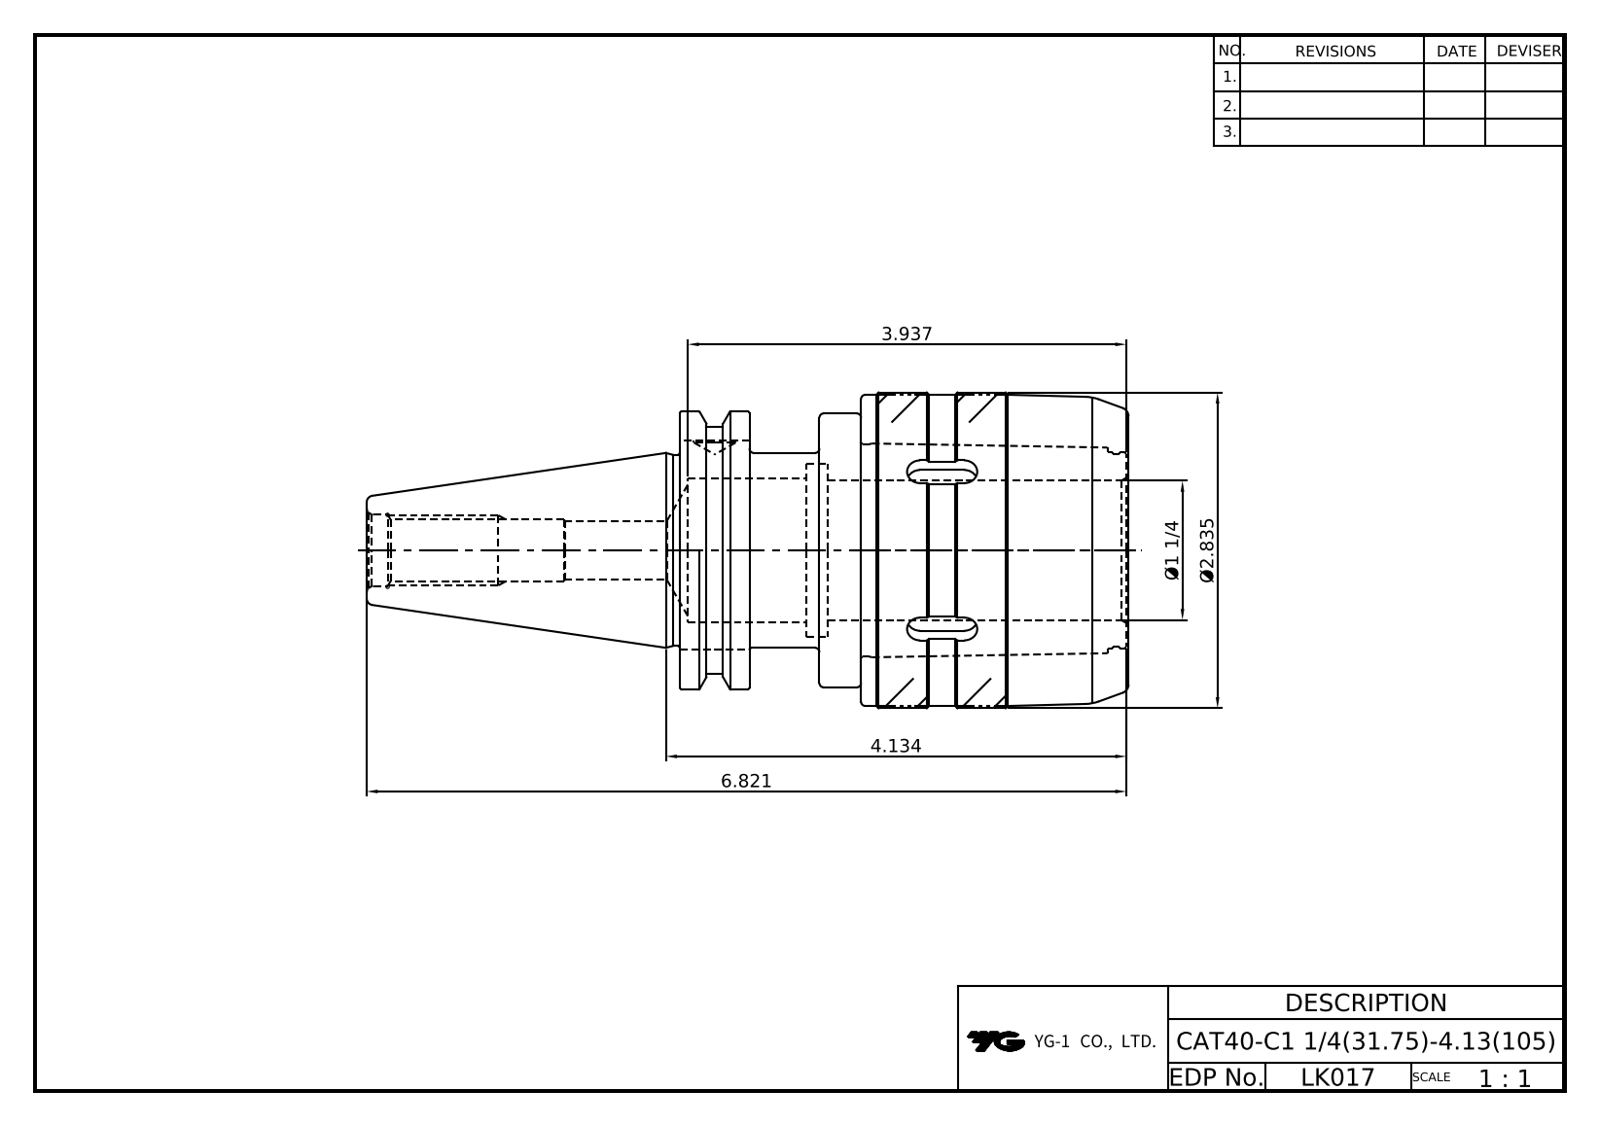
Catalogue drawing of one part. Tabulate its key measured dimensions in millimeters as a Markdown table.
| quantity | value |
| --- | --- |
| part name | LO-CAT40-C31.75-105; C32-CAP |
| STEP written by | Autodesk Inventor 2020 (AUTOMOTIVE_DESIGN) |
| units | millimeters |
| bodies | 2 solids, 194 faces (86 planar, 48 cylindrical, 60 other) |
| overall size | 173.75 × 72 × 72 |
| volume | 282 092 mm³ |
| surface area | 76 025 mm² |
| round holes (diameter × count) | 9.53 × 1, 13 × 1, 13.39 × 1, 16.3 × 1, 33 × 1, 39.5 × 1, 55.6 × 1, 56 × 1, 58 × 1 |
| round bosses / shafts (diameter × count) | 72 × 1, 71 × 1, 63.5 × 1, 62.5 × 1, 56.3 × 1, 49.4 × 1, 48.34 × 1, 45 × 1 |
| partial cylindrical surfaces (radius × count) | 3 × 6 |
| main face-to-face distances | 41.33, 31.83, 9.5, 15.88, 15.95, 25.45, 102.33, 86.45, 70.5, 61 |
